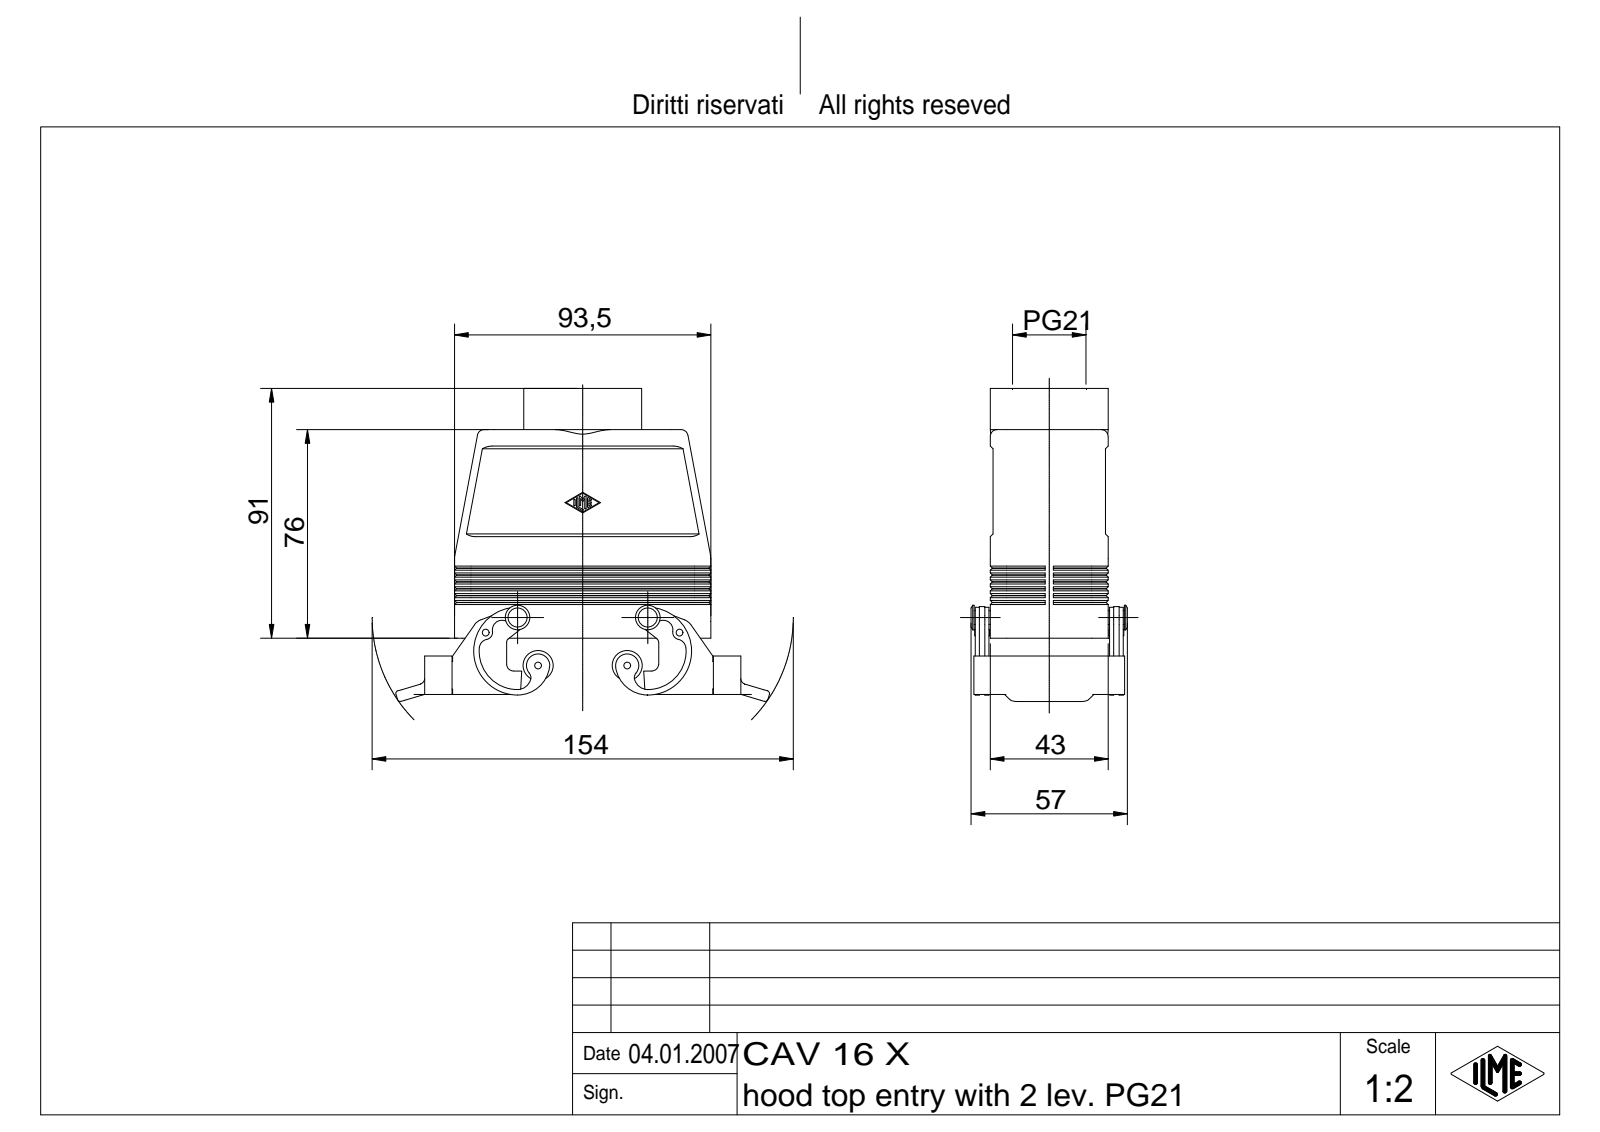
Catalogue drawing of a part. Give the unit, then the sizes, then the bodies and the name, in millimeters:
Units: millimetres
Overall size (bounding box): 136.29 × 114.08 × 57
Round holes (diameter × count): ⌀2.5 ×2, ⌀24.78 ×1, ⌀26.78 ×1
Round bosses / shafts (diameter × count): ⌀11 ×2, ⌀9 ×2, ⌀5 ×2, ⌀2 ×2, ⌀43 ×1, ⌀25.78 ×1
Partial cylindrical surfaces — rounded edges, fillets, slot ends (radius × count): R0.25 ×14, R1 ×12, R2 ×10, R2.5 ×10, R6 ×10, R3 ×8, R3.5 ×4, R5 ×4
Main face-to-face distances: 3, 2, 42, 37, 40, 1, 39, 43, 5, 41
Hole centre spacings: 70.7
Volume: 104 872 mm³ · Surface area: 62 927 mm²
Bodies: 1 solid, 945 faces (282 planar, 248 cylindrical, 415 other)
Part name (STEP PRODUCT): CAV Tüllengehäuse 2 Bügel für einen Einsatz Teil A
STEP written by: Autodesk Inventor 7 (AUTOMOTIVE_DESIGN)
